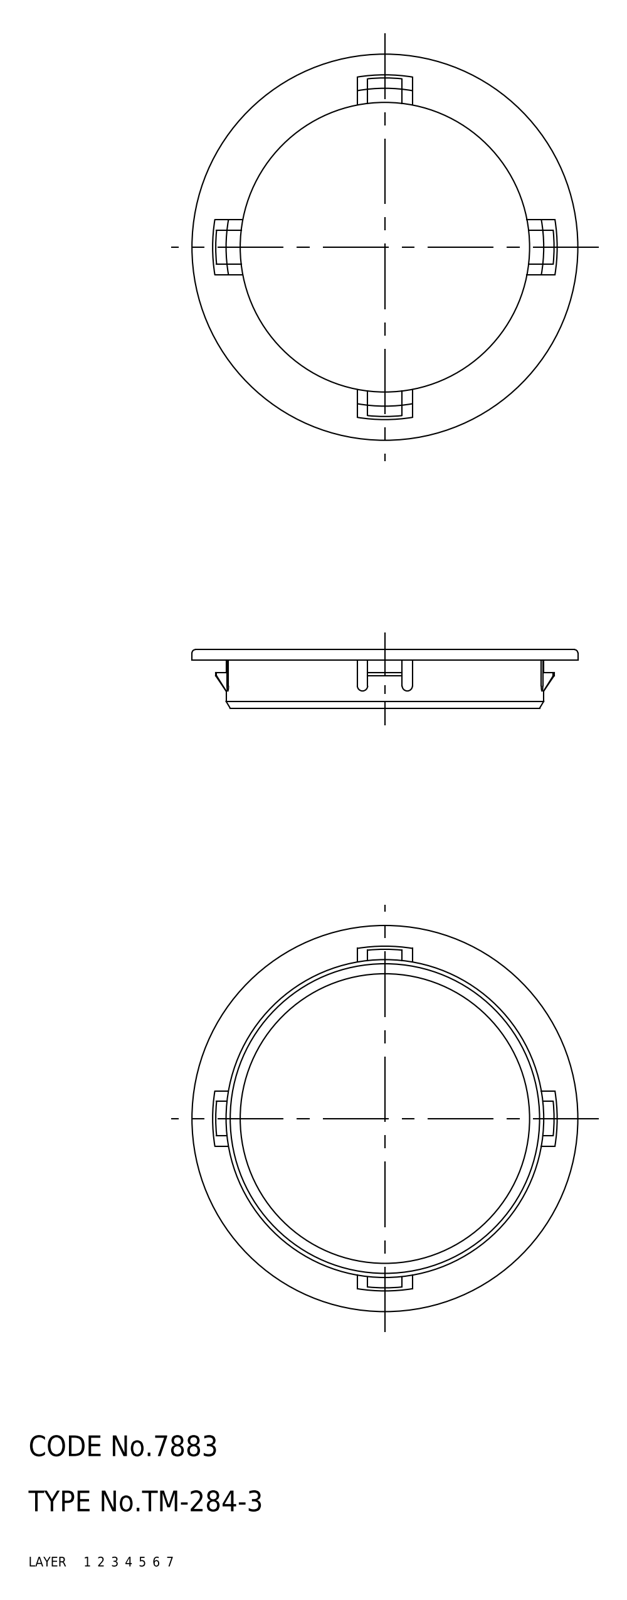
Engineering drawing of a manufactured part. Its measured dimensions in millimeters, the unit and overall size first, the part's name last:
Units: millimetres
Overall size (bounding box): 56 × 56 × 8.5
Volume: 3 379 mm³ · Surface area: 4 554 mm²
Bodies: 1 solid, 61 faces (0 planar, 0 cylindrical, 61 other)
Part name (STEP PRODUCT): grommet
STEP written by: CADfix (AUTOMOTIVE_DESIGN)
